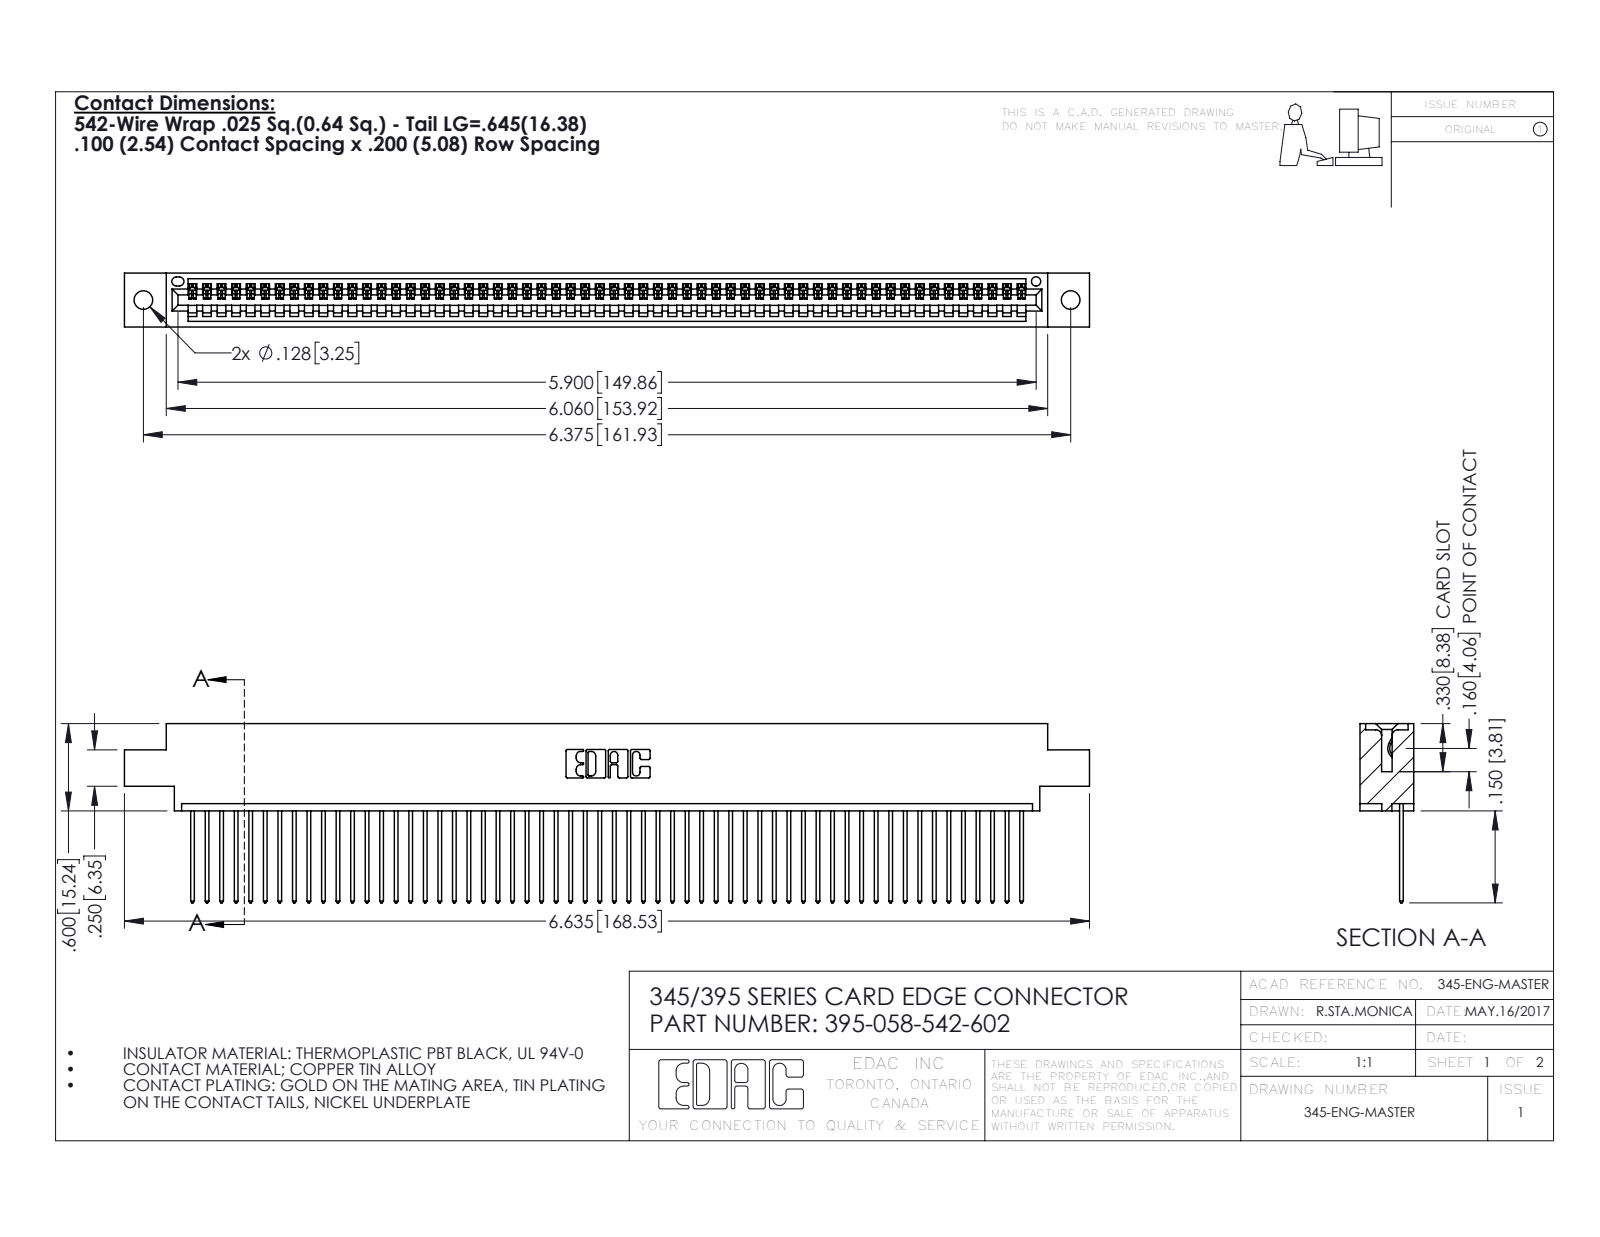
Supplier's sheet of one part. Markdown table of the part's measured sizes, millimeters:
| quantity | value |
| --- | --- |
| part name | 345 Part_0.170 Offset - 0.128 Dia; 395-058-542-602; 345-292-001_345-293-142 |
| STEP written by | SolidWorks 2016 (CONFIG_CONTROL_DESIGN) |
| units | millimeters |
| bodies | 59 solids, 3494 faces (2404 planar, 1090 cylindrical, 0 other) |
| overall size | 168.5 × 31.3 × 9.4 |
| volume | 16 100 mm³ |
| surface area | 22 310 mm² |
| round holes (diameter × count) | 3.3 × 2, 1.6 × 1 |
| partial cylindrical surfaces (radius × count) | 0.2 × 116, 0.3 × 116, 0.3 × 22, 0.2 × 6, 0.8 × 6, 0.7 × 3, 0.8 × 2, 1 × 2 |
| main face-to-face distances | 1.8, 7.6, 9.4, 2.5, 6.9, 0.6, 5.1, 5.7, 4.4, 3.8 |
| hole center spacings | 6.9, 155.9, 161.9 |
